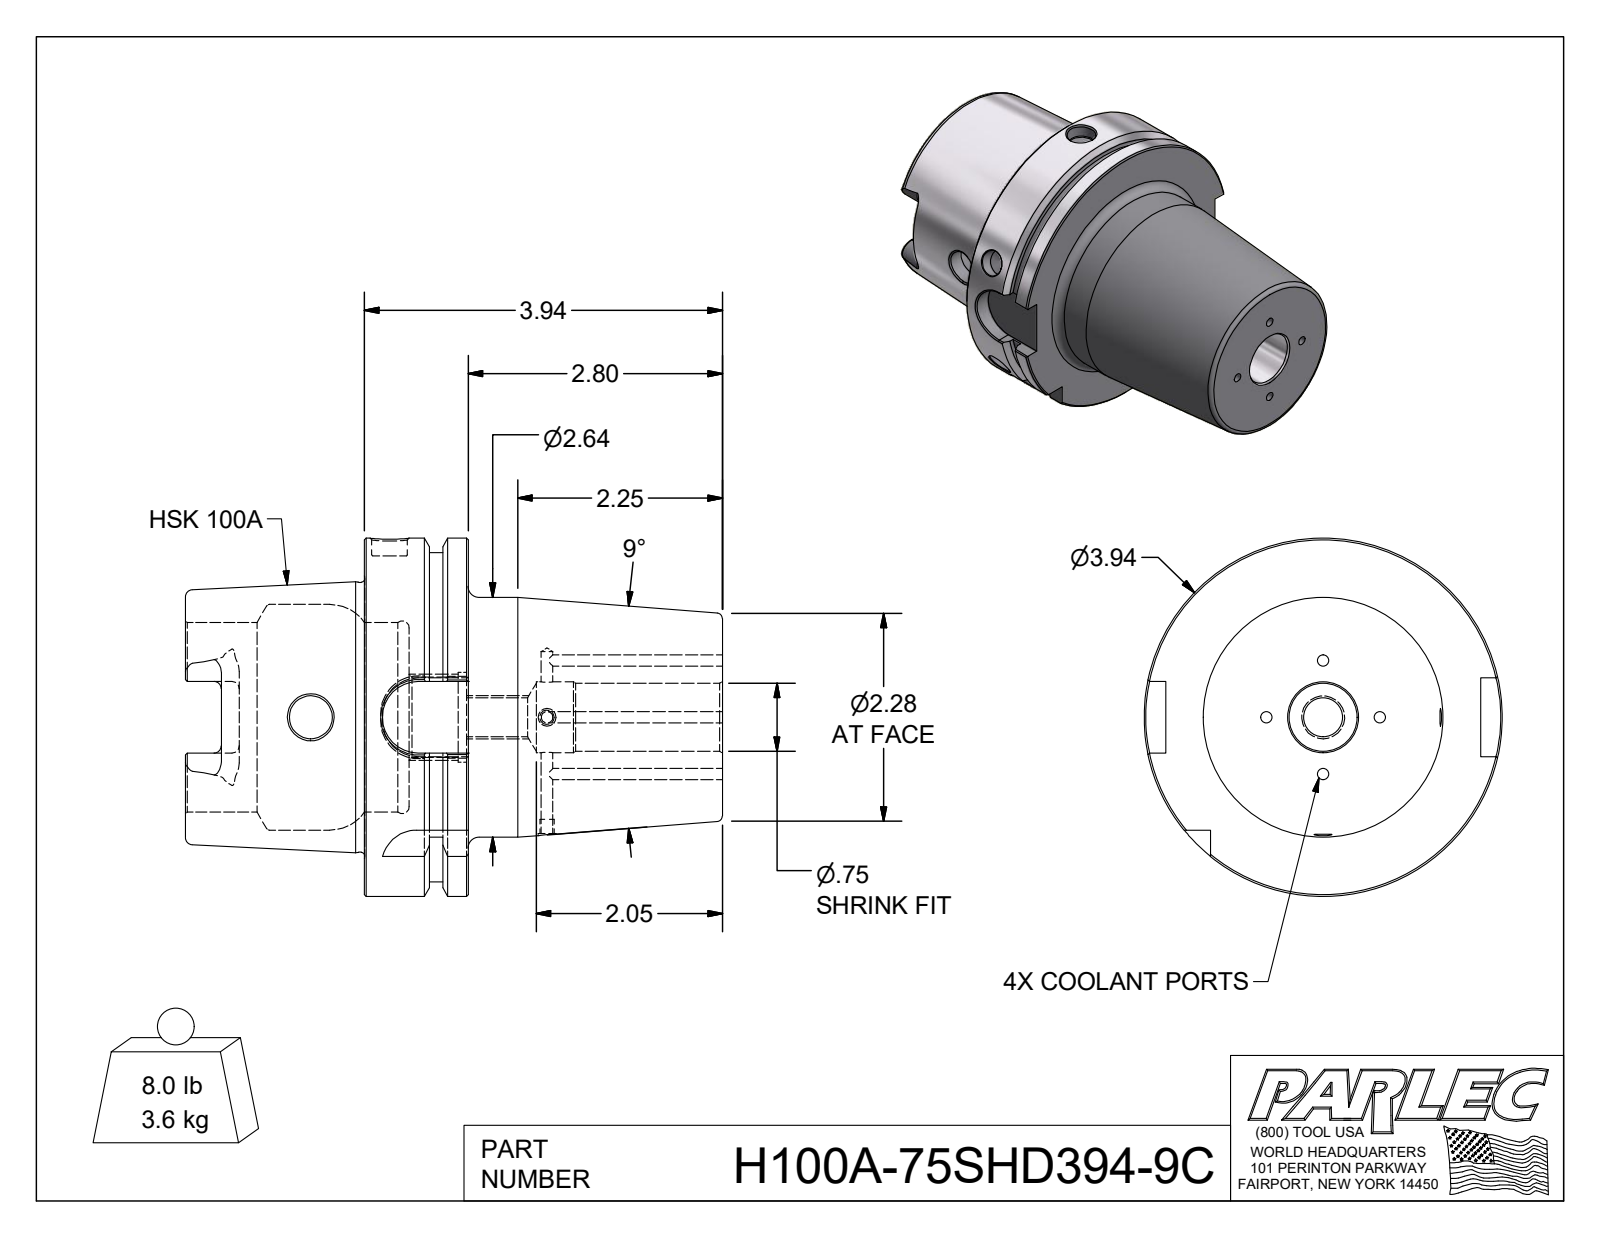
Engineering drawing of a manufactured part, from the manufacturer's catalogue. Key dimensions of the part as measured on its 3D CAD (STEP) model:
STEP written by: Autodesk Inventor 2018 (AUTOMOTIVE_DESIGN)
Units: inches
Bodies: 1 solid, 163 faces (57 planar, 46 cylindrical, 60 other)
Overall size (bounding box): 5.906 × 3.937 × 3.937
Volume: 28.05 in³ · Surface area: 106.9 in²
Round holes (diameter × count): ⌀0.125 ×4, ⌀0.128 ×2, ⌀0.197 ×2, ⌀0.354 ×2, ⌀0.394 ×1, ⌀0.43 ×1, ⌀0.472 ×1, ⌀0.749 ×1, ⌀0.779 ×1, ⌀0.881 ×1, ⌀0.985 ×1, ⌀2.087 ×1
Round bosses / shafts (diameter × count): ⌀3.937 ×1, ⌀3.622 ×1, ⌀2.967 ×1, ⌀2.638 ×1
Partial cylindrical surfaces — rounded edges, fillets, slot ends (radius × count): R0.079 ×6, R0.192 ×4, R0.394 ×4
Main face-to-face distances: 1.142, 3.937, 2.795, 0.492, 0.65, 3.445, 1.969, 2.461, 3.11, 5.906
Hole centre spacings: 0.625, 0.884, 0.884, 0.625, 1.25, 1.25, 1.732, 2.598
